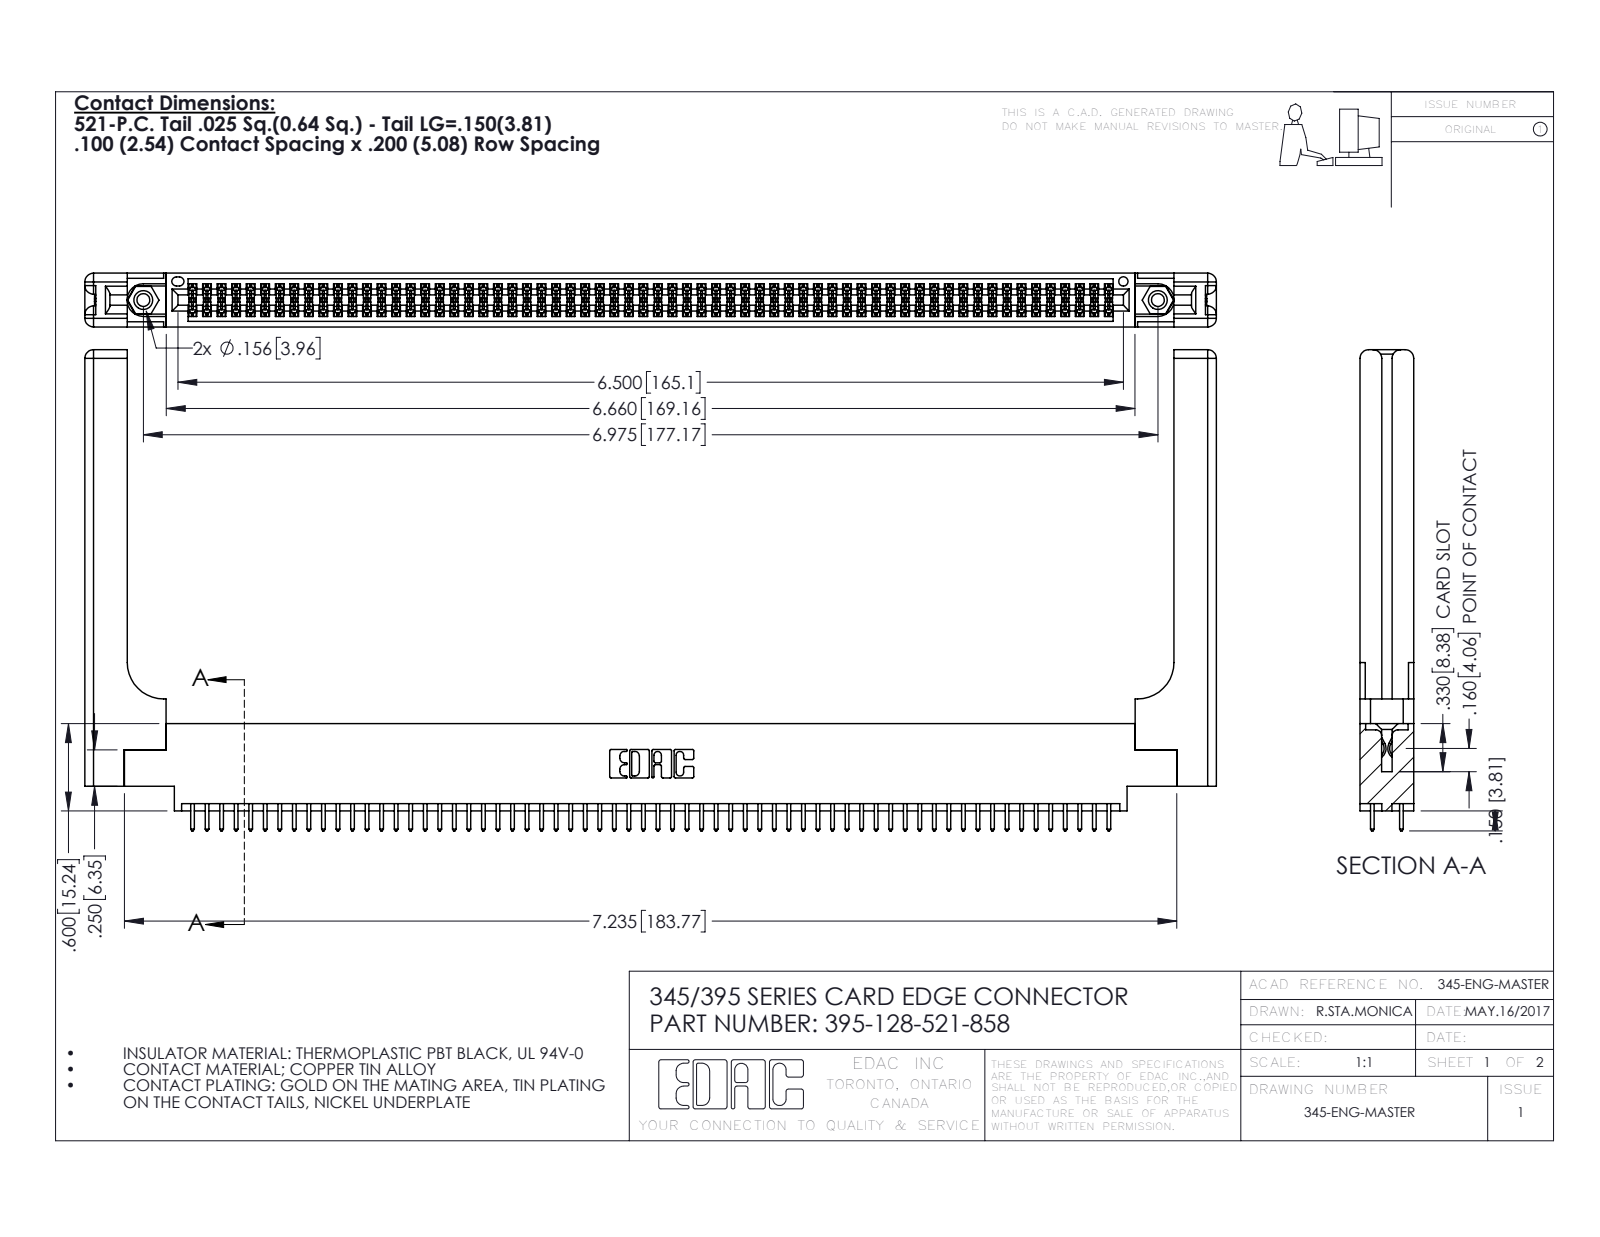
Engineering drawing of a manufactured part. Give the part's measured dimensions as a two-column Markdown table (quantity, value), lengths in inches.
| quantity | value |
| --- | --- |
| part name | 345 Part_0.170 Offset - 0.156 Dia-TH; 345-250-001_345-250-001-102; 345-292-001_345-293-121; 395-128-521-858 (+1 more) |
| STEP written by | SolidWorks 2016 (CONFIG_CONTROL_DESIGN) |
| units | inches |
| bodies | 133 solids, 6786 faces (4456 planar, 2270 cylindrical, 60 other) |
| overall size | 7.779 × 3.307 × 0.37 |
| volume | 1.691 in³ |
| surface area | 52.26 in² |
| round holes (diameter × count) | 0.089 × 2, 0.125 × 2, 0.156 × 2, 0.064 × 1 |
| round bosses / shafts (diameter × count) | 0.155 × 2 |
| partial cylindrical surfaces (radius × count) | 0.006 × 192, 0.01 × 128, 0.01 × 22, 0.06 × 16, 0.007 × 6, 0.031 × 6, 0.026 × 3, 0.014 × 2 |
| main face-to-face distances | 0.072, 0.298, 0.37, 0.098, 0.272, 0.025, 0.2, 0.225, 0.175, 0.148 |
| hole center spacings | 0.27, 6.739, 6.975 |
